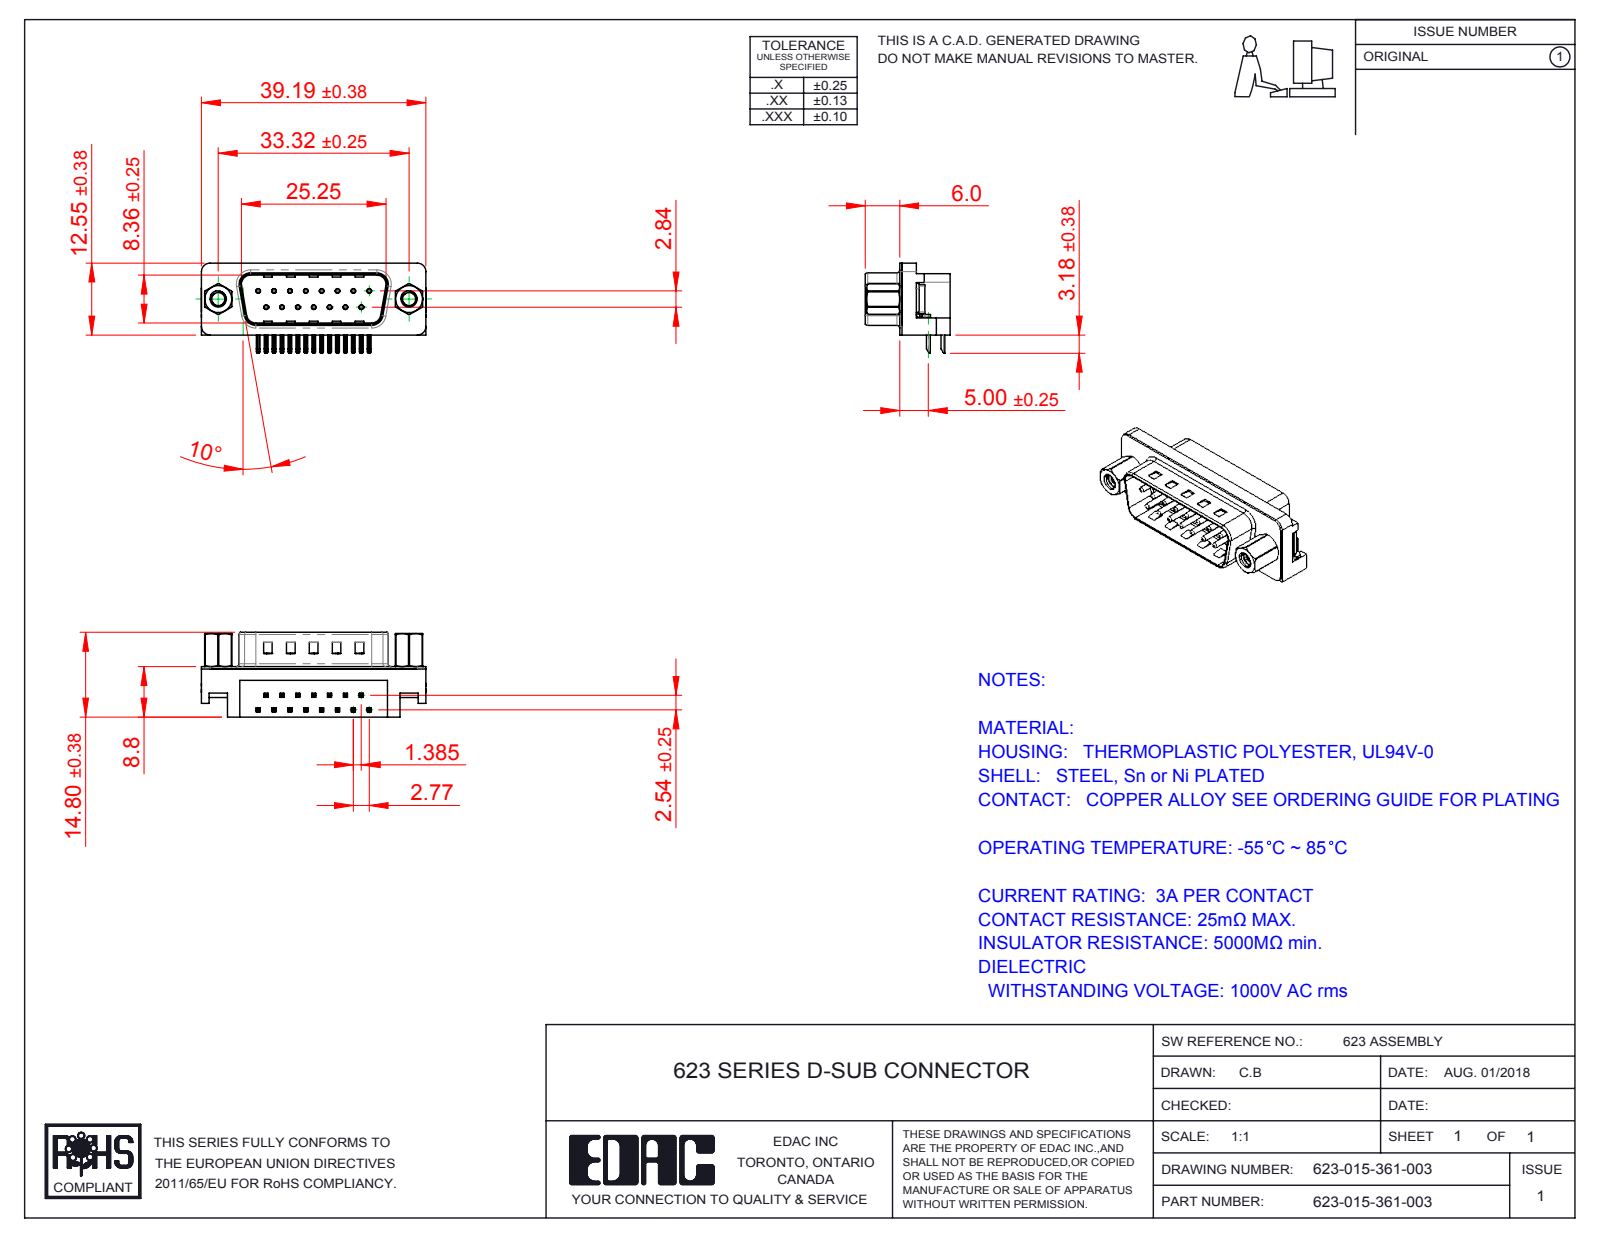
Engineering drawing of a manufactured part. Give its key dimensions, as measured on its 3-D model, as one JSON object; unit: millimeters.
{"part_name": "623 Housing_15 Socket; 623 Contact Bottom; 623 Shell_15 Socket; 623 4-40 Hex Standoff 5 (+4 more)", "step_written_by": "SolidWorks 2016 (CONFIG_CONTROL_DESIGN)", "units": "millimeters", "bodies": {"solids": 23, "faces": 1591, "planar": 915, "cylindrical": 503, "other": 173}, "overall_size": [39.22, 15.73, 14.8], "volume_mm3": 3527, "surface_area_mm2": 5355, "round_holes": [[0.35, 15], [0.8, 15], [2.26, 2], [2.29, 2], [4, 2], [4.8, 2], [5, 2]], "round_bosses_or_shafts": [[0.75, 15], [4.9, 2], [4.75, 2], [3.9, 2], [2.79, 2]], "partial_cylinders_radius": [[0.25, 68], [0.12, 30], [1, 16], [0.5, 9], [1.5, 6], [0.9, 4], [1.6, 4], [2, 4]], "face_to_face_distances": [0.4, 8.4, 8.8, 2.1, 1.7, 10.46, 10.86, 8.76, 5.9, 2.9], "hole_center_spacings": [3.16, 2.77, 5.54, 8.31, 11.08, 5.03, 5.04, 7.48]}
